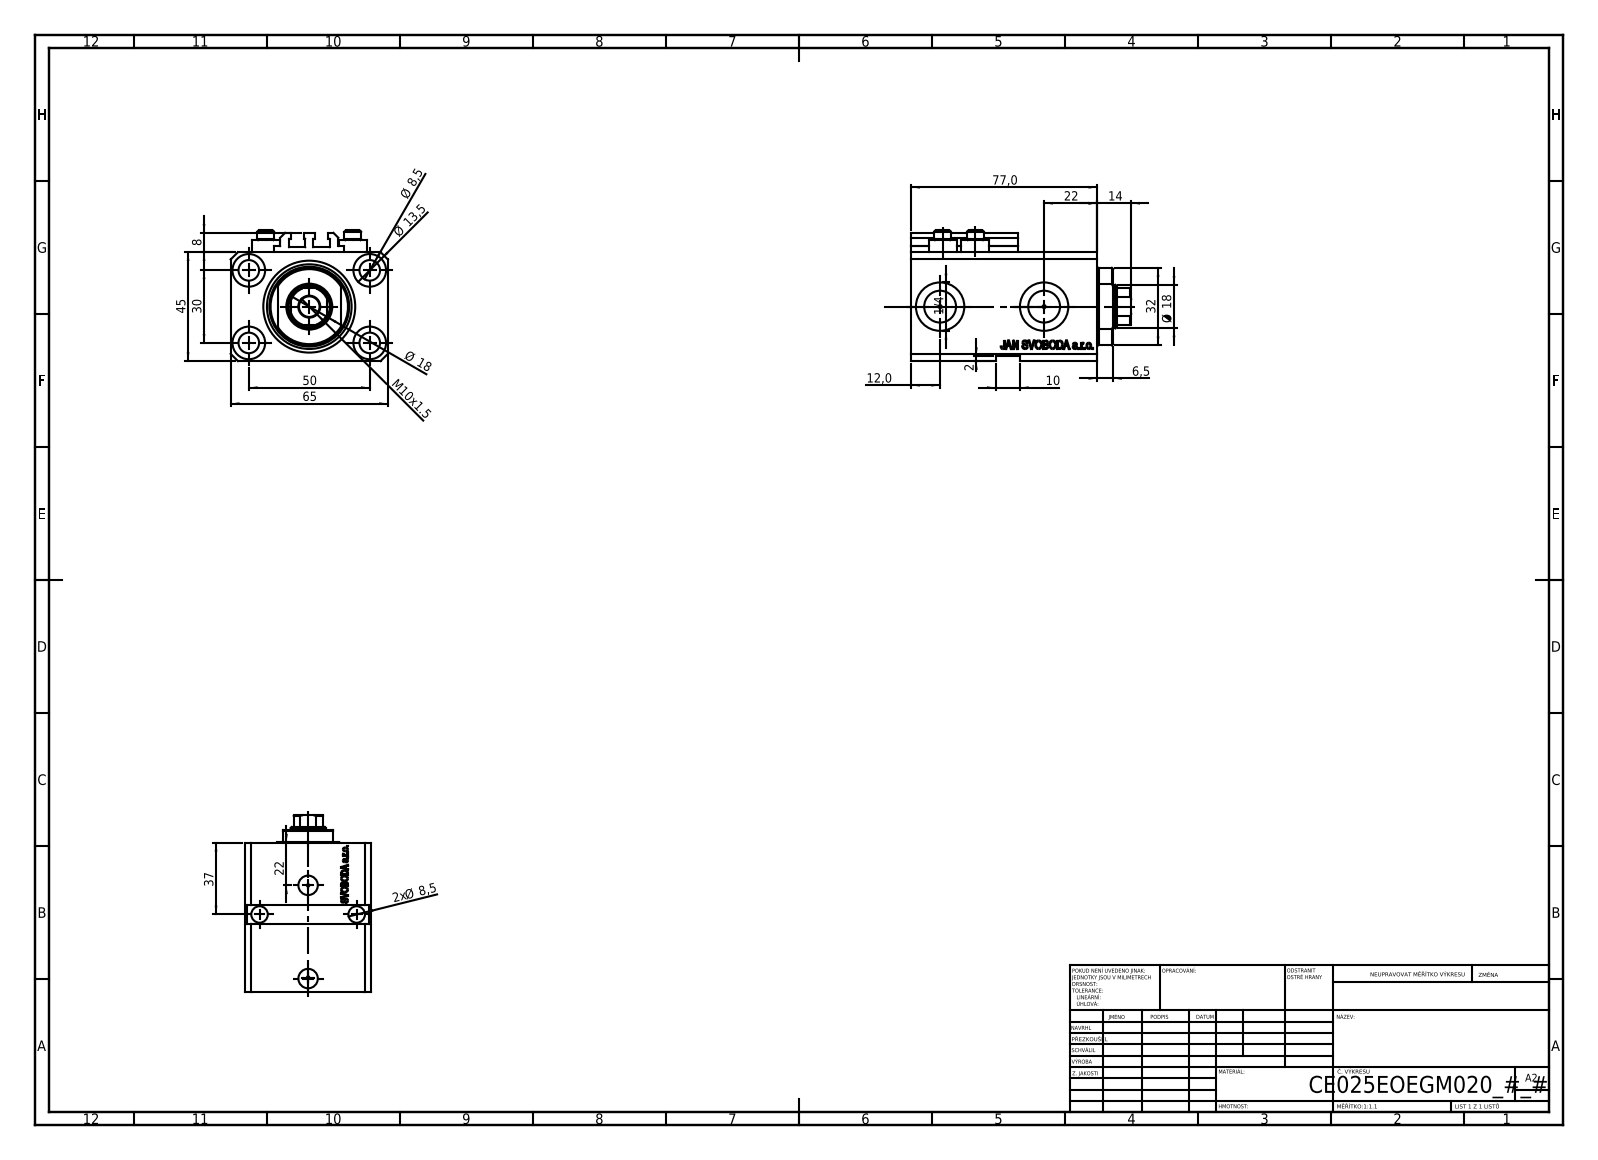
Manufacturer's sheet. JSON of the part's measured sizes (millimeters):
{"part_name": "V250CE_E_Body; V250CE_C_VCP; ALLEN BOLT V250CE; V250CE_VC_E", "step_written_by": "SolidWorks 2019 (CONFIG_CONTROL_DESIGN)", "units": "millimeters", "bodies": {"solids": 8, "faces": 1067, "planar": 511, "cylindrical": 126, "other": 430}, "overall_size": [91, 65, 54], "volume_mm3": 199775, "surface_area_mm2": 59185, "round_holes": [[8.5, 7], [1.25, 4], [4, 4], [13.5, 4], [10, 2], [13.16, 2], [20, 2], [18, 1], [25, 1], [38, 1]], "round_bosses_or_shafts": [[11.6, 4], [7, 4]], "partial_cylinders_radius": [[0.2, 10], [8.5, 1], [16, 1]], "face_to_face_distances": [45, 65, 63, 14, 77, 2, 6.9, 56.1, 70.1, 47], "hole_center_spacings": [29.15, 50, 13.6, 15.12, 18.81, 18.97, 26.22, 26.61]}
